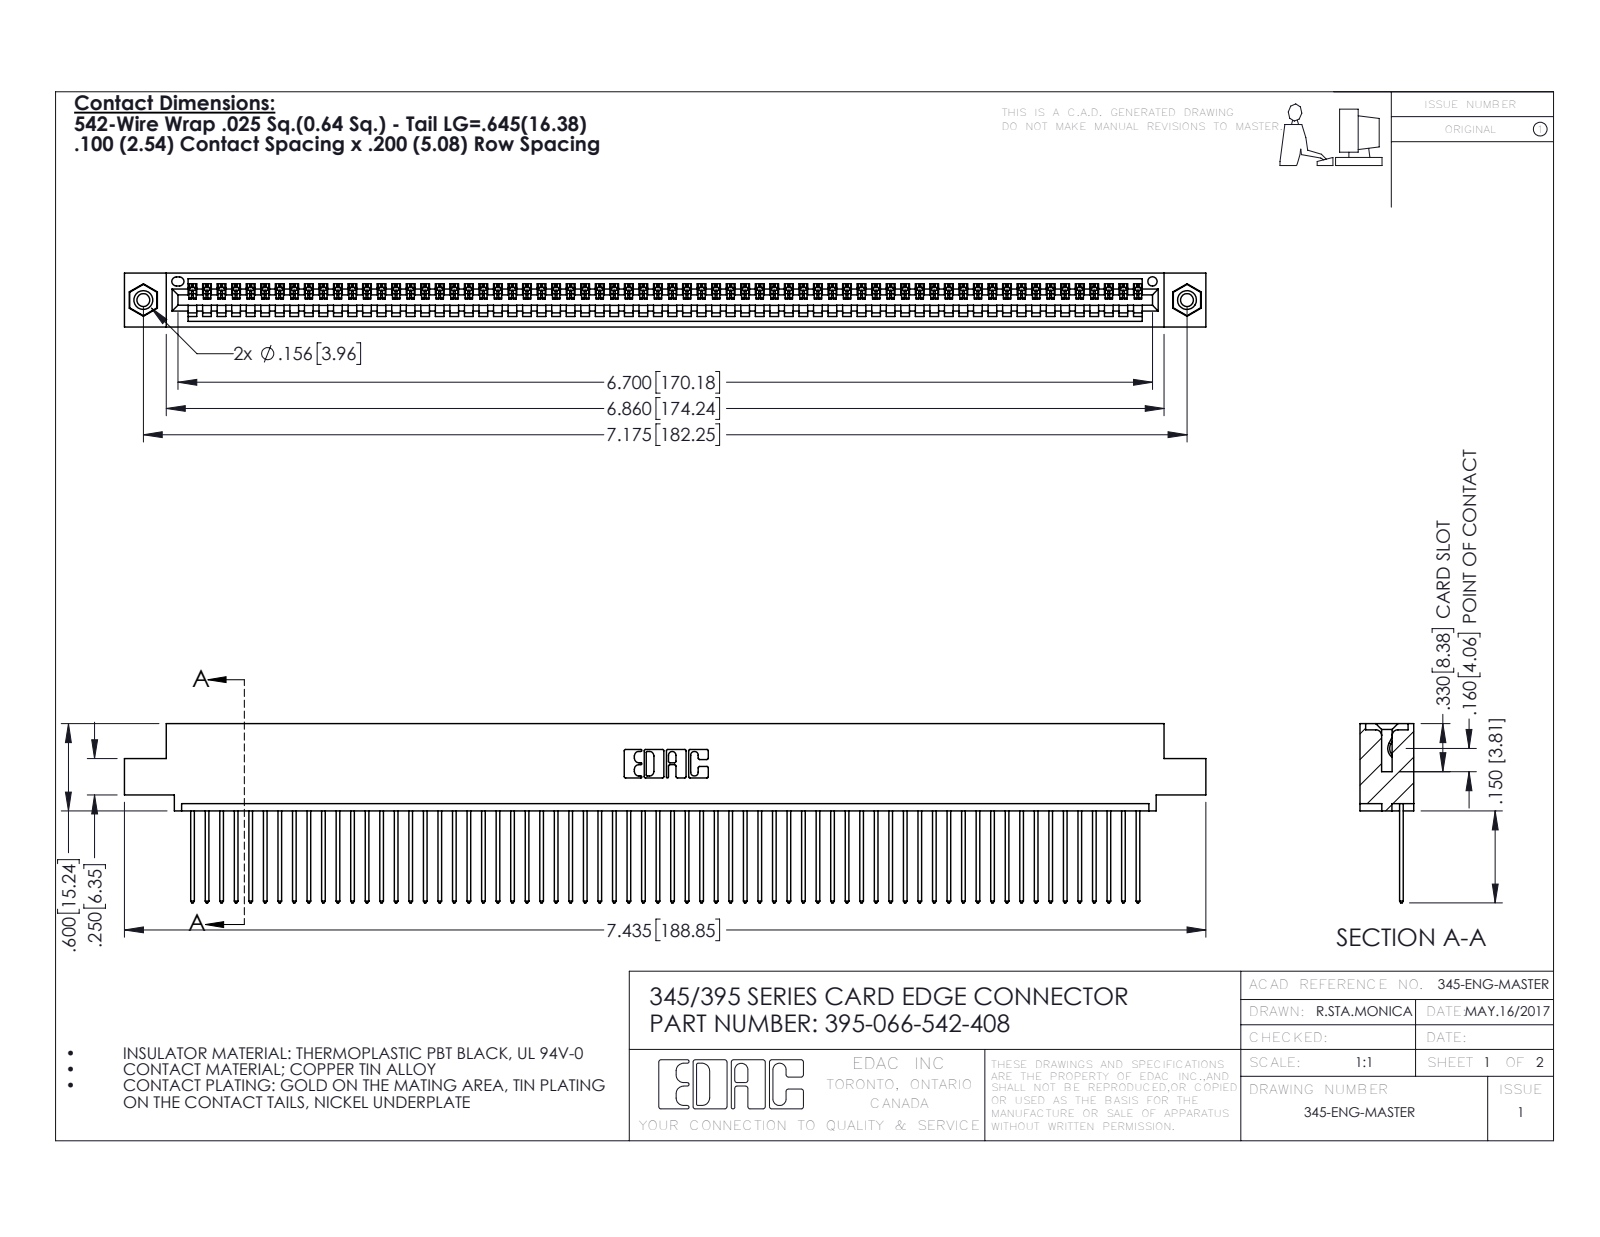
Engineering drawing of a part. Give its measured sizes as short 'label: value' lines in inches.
name: 345-292-001_345-293-142; 345 Part_0.110 Offset - 0.156 Dia-TI; 395-066-542-408; 345-250-001_345-250-003-102
written by: SolidWorks 2016 (CONFIG_CONTROL_DESIGN)
unit: in
bodies: 69 solids, 4018 faces (2756 planar, 1246 cylindrical, 16 other)
size: 7.435 × 1.232 × 0.37
volume: 1.111 in³; area: 39.59 in²
holes: 2× ⌀0.089, 2× ⌀0.125, 2× ⌀0.156, 1× ⌀0.064
bosses: 2× ⌀0.155
rounds: 132× R0.006, 132× R0.01, 22× R0.01, 6× R0.007, 6× R0.031, 3× R0.026, 2× R0.031, 2× R0.04
face distances: 0.072, 0.298, 0.098, 0.272, 0.025, 0.37, 0.2, 0.225, 0.149, 0.072
hole spacings: 0.27, 6.939, 7.175
